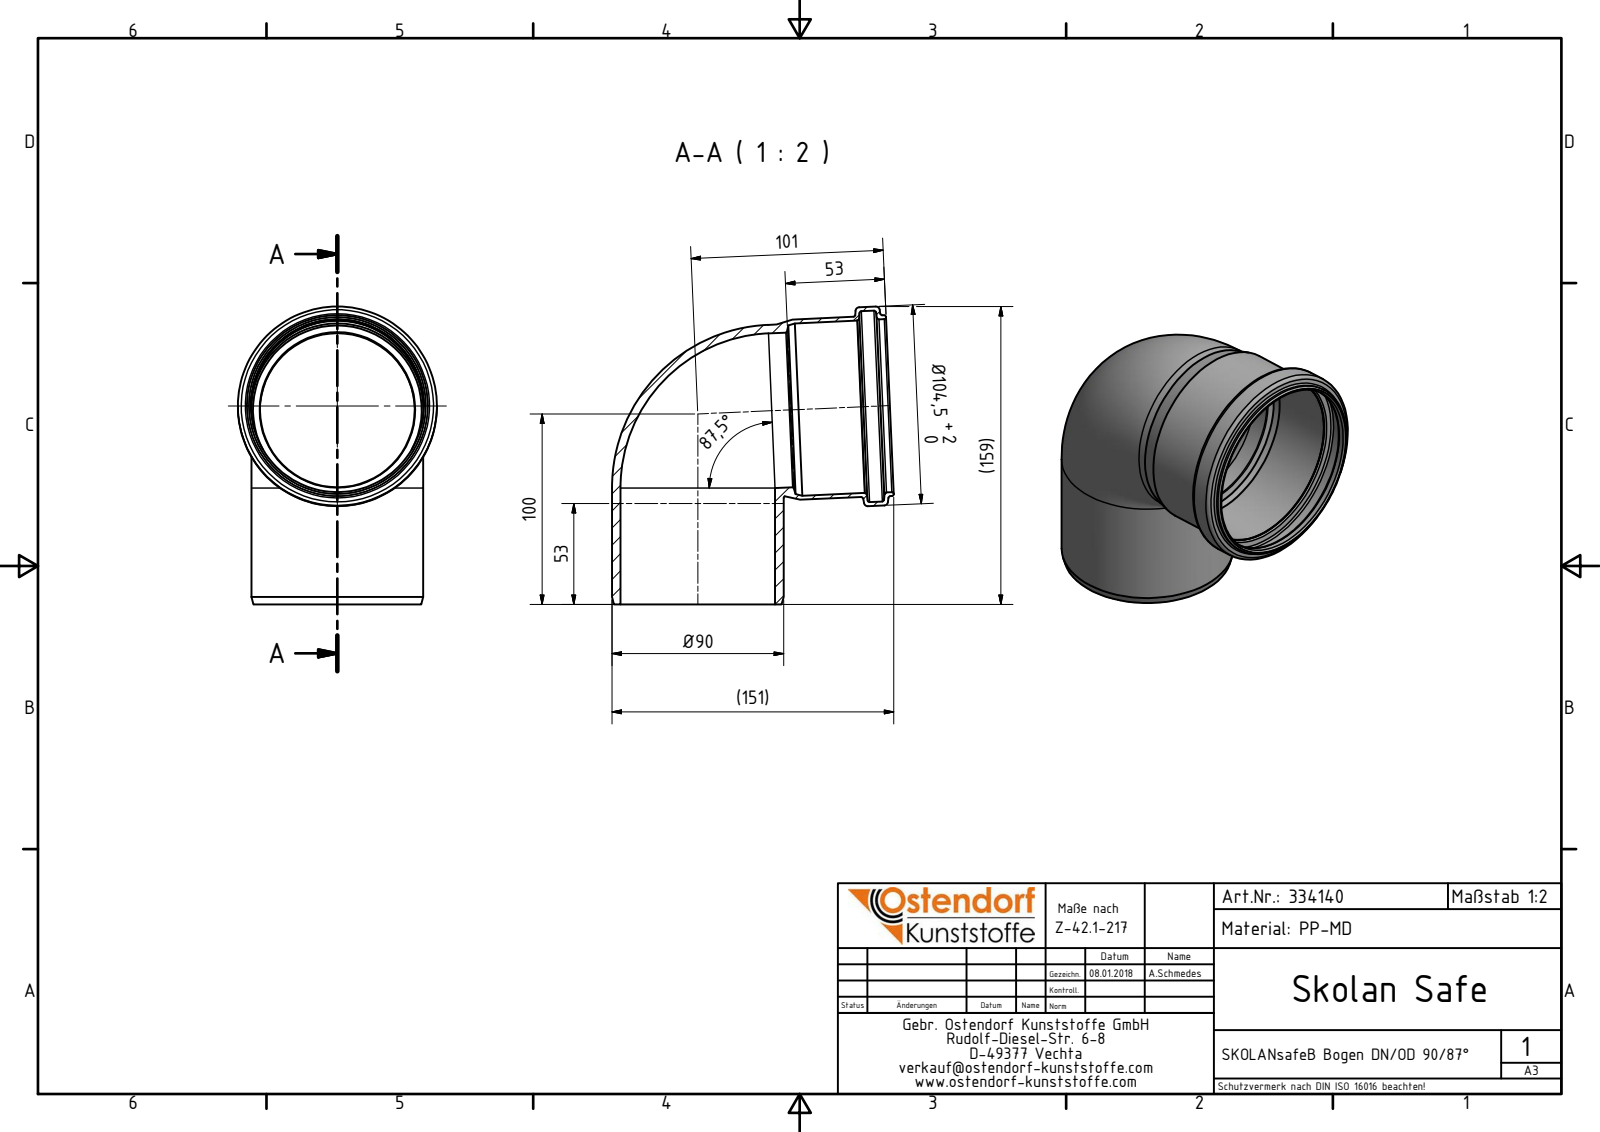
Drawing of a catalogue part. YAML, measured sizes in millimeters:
part_name: "334140 SKOLANsafeB Bogen DN_OD 90_87°"
step_written_by: "Autodesk Inventor 2016 (AUTOMOTIVE_DESIGN)"
units: millimeters
bodies: {solids: 1, faces: 36, planar: 3, cylindrical: 11, other: 22}
overall_size: [156.38, 148.03, 104.5]
volume: 186305
surface_area: 109156
round_holes:
  - {diameter: 81.2, count: 2}
  - {diameter: 90.5, count: 1}
  - {diameter: 90.8, count: 1}
  - {diameter: 100.3, count: 1}
round_bosses_or_shafts:
  - {diameter: 90.2, count: 2}
  - {diameter: 104.5, count: 1}
  - {diameter: 95, count: 1}
  - {diameter: 94.7, count: 1}
face_to_face_distances: [15.21]
